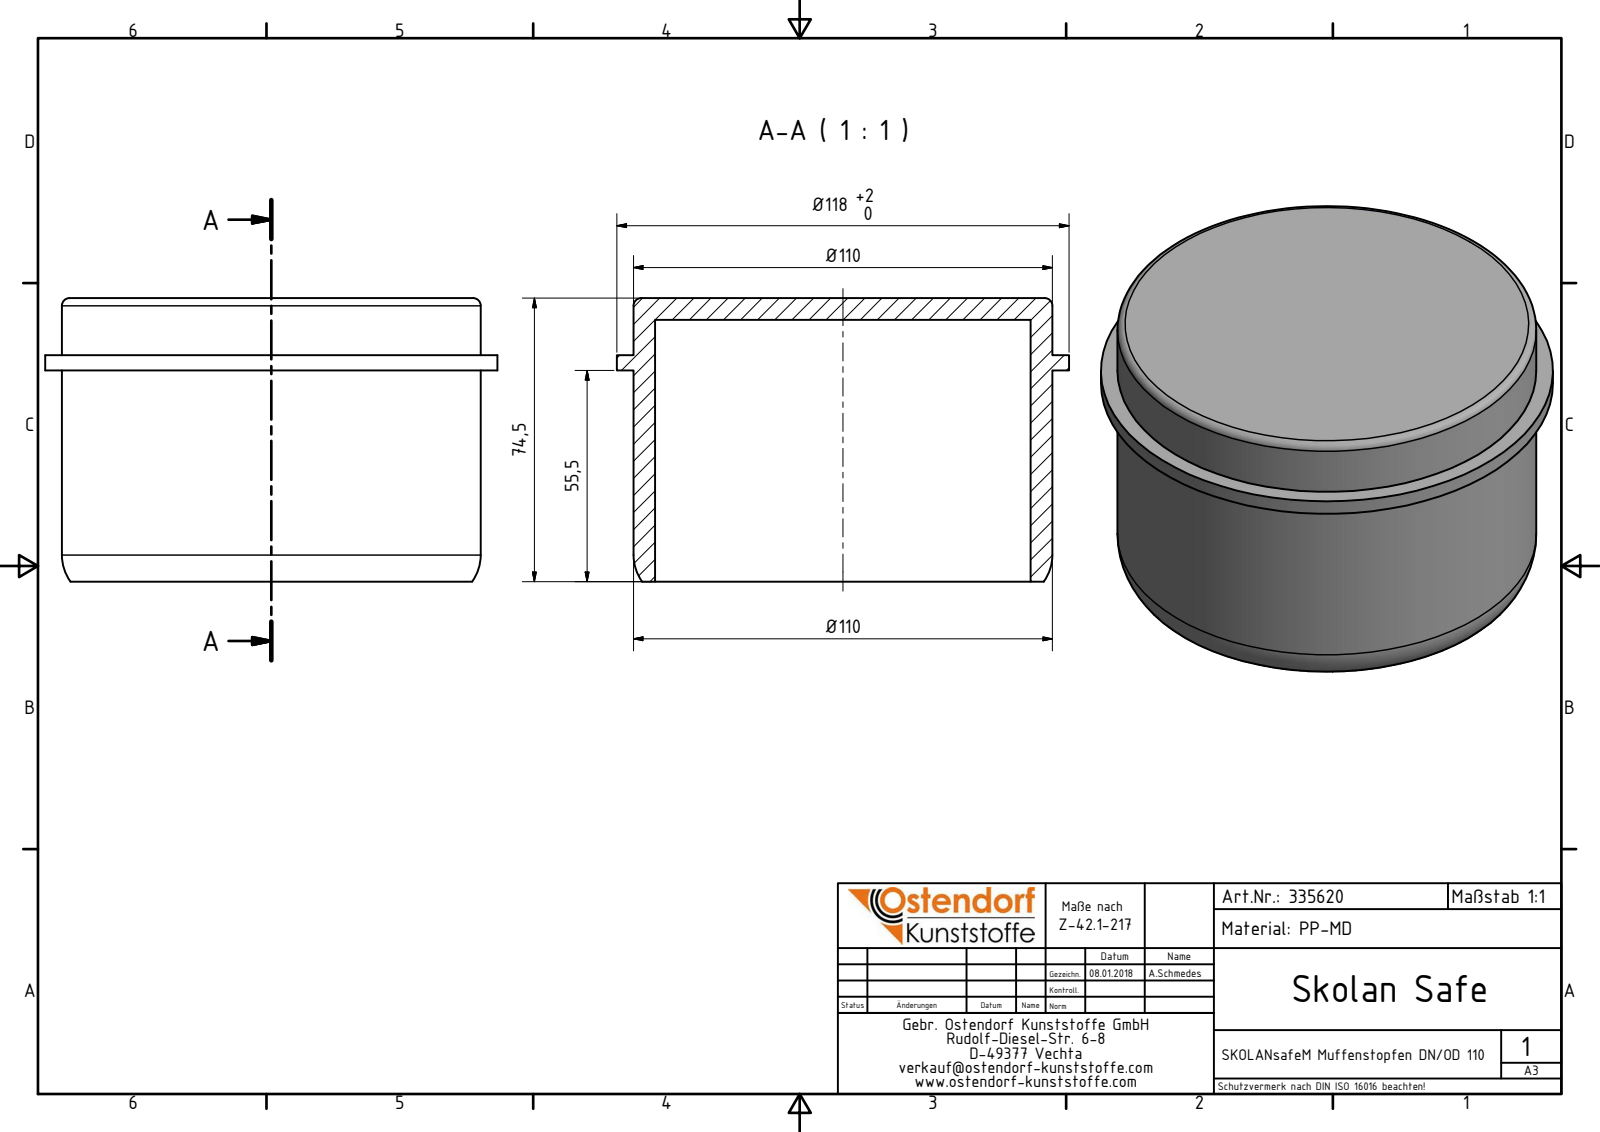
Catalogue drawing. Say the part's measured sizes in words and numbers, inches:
The part is named "335620 SKOLANsafeM Muffenstopfen DN_OD 110". Its 3-D file was written by "Autodesk Inventor 2016 (AUTOMOTIVE_DESIGN)". It is 1 solid with 11 faces: 5 planar, 4 cylindrical and 2 other. Overall it measures 4.673 by 4.673 by 2.929 inches. Its volume is 11.39 cubic inches and its surface area 105.9 square inches. Round holes: 1 of diameter 3.882. Round bosses or shafts: 1 of diameter 4.673, 1 of diameter 4.331. The main face-to-face distances are 0.224, 0.157, 0.524, 0.748, 0.366, 0.591, 2.181, 2.339, 2.705, 2.929.
